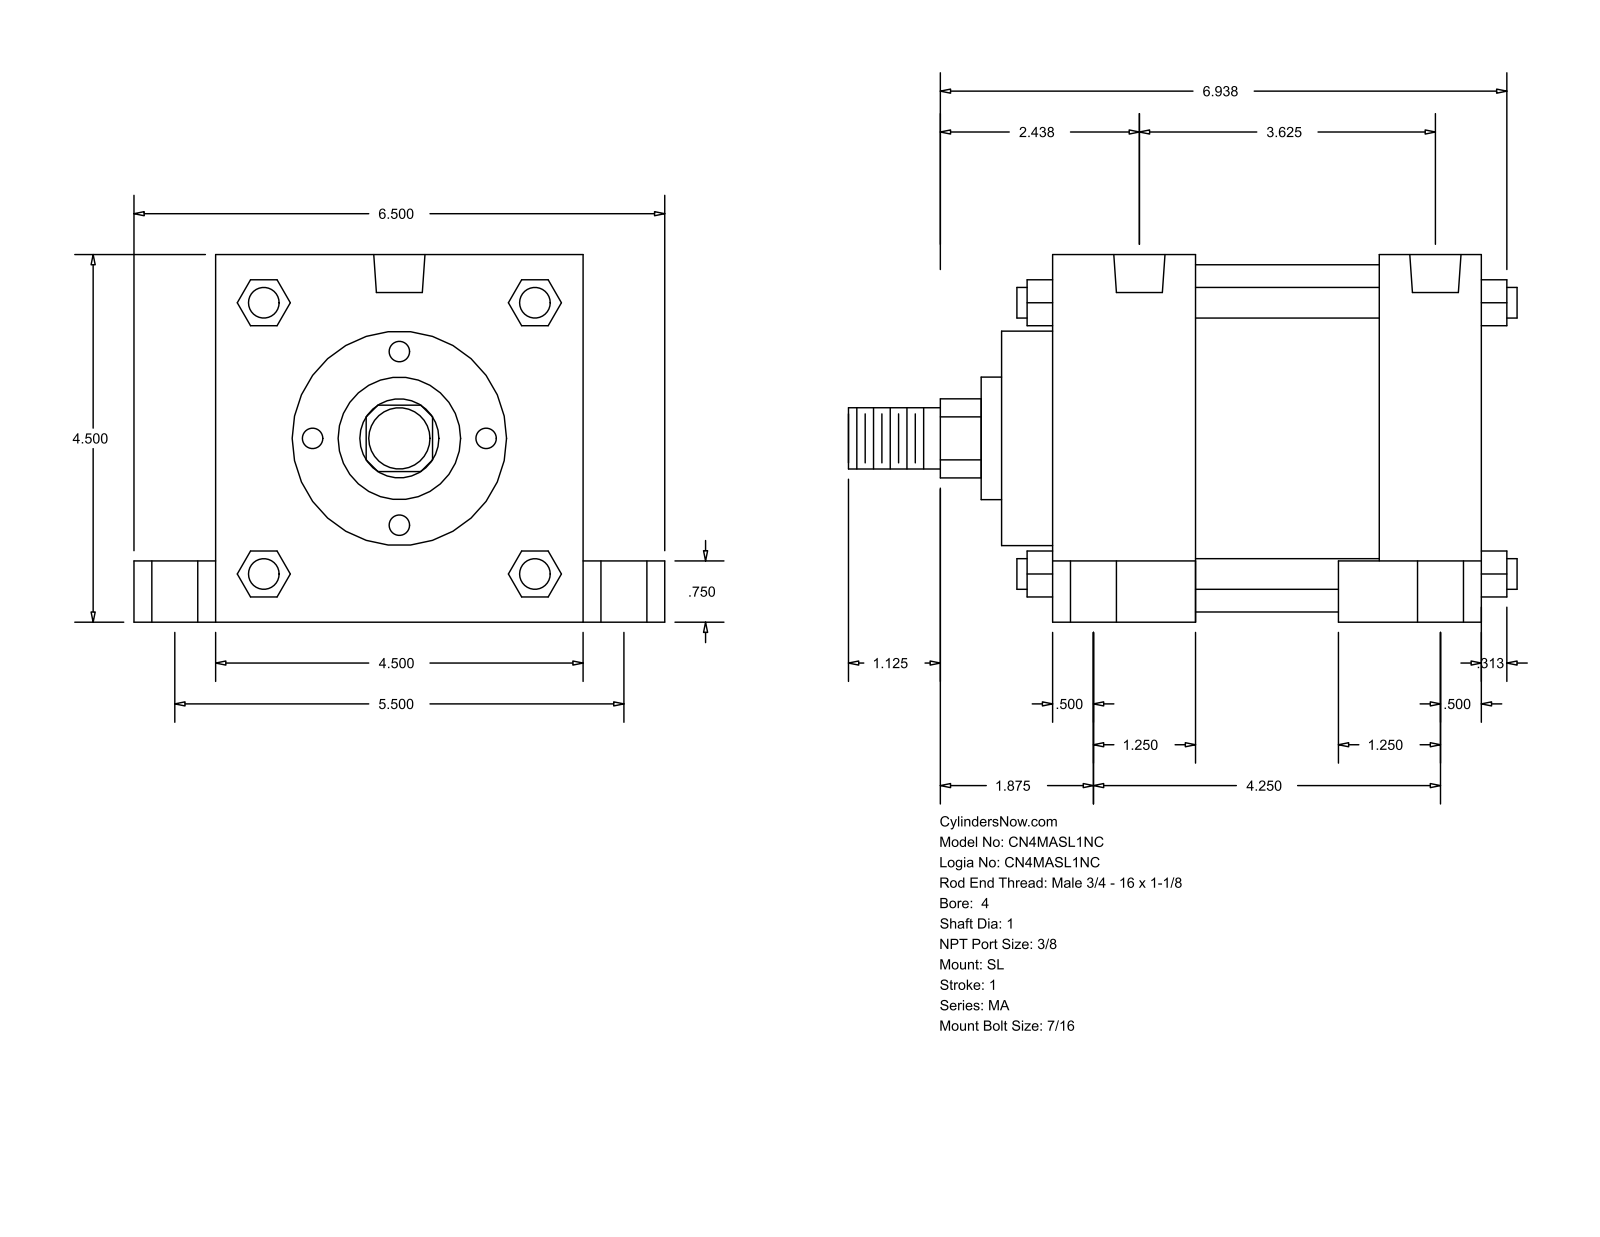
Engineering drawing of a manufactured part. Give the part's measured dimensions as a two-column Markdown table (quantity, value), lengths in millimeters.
| quantity | value |
| --- | --- |
| part name | MA_SL__0400_1 |
| STEP written by | GSSL Pune (CONFIG_CONTROL_DESIGN) |
| units | millimeters |
| bodies | 0 solids, 150 faces (113 planar, 37 cylindrical, 0 other) |
| overall size | 207.96 × 165.1 × 114.3 |
| round holes (diameter × count) | 11.11 × 4, 14.29 × 4, 20.64 × 4, 15.93 × 2 |
| round bosses / shafts (diameter × count) | 9.53 × 4, 107.95 × 1, 66.67 × 1, 38.1 × 1, 25.4 × 1, 19.05 × 1 |
| partial cylindrical surfaces (radius × count) | 12.29 × 1 |
| main face-to-face distances | 114.3, 133.36, 57.15, 44.46, 88.9, 101.61, 31.75, 25.4, 139.7, 19.05 |
| hole center spacings | 69.87, 70.14, 71.3, 72.4, 82.55, 107.95, 113.06, 116.84 |
